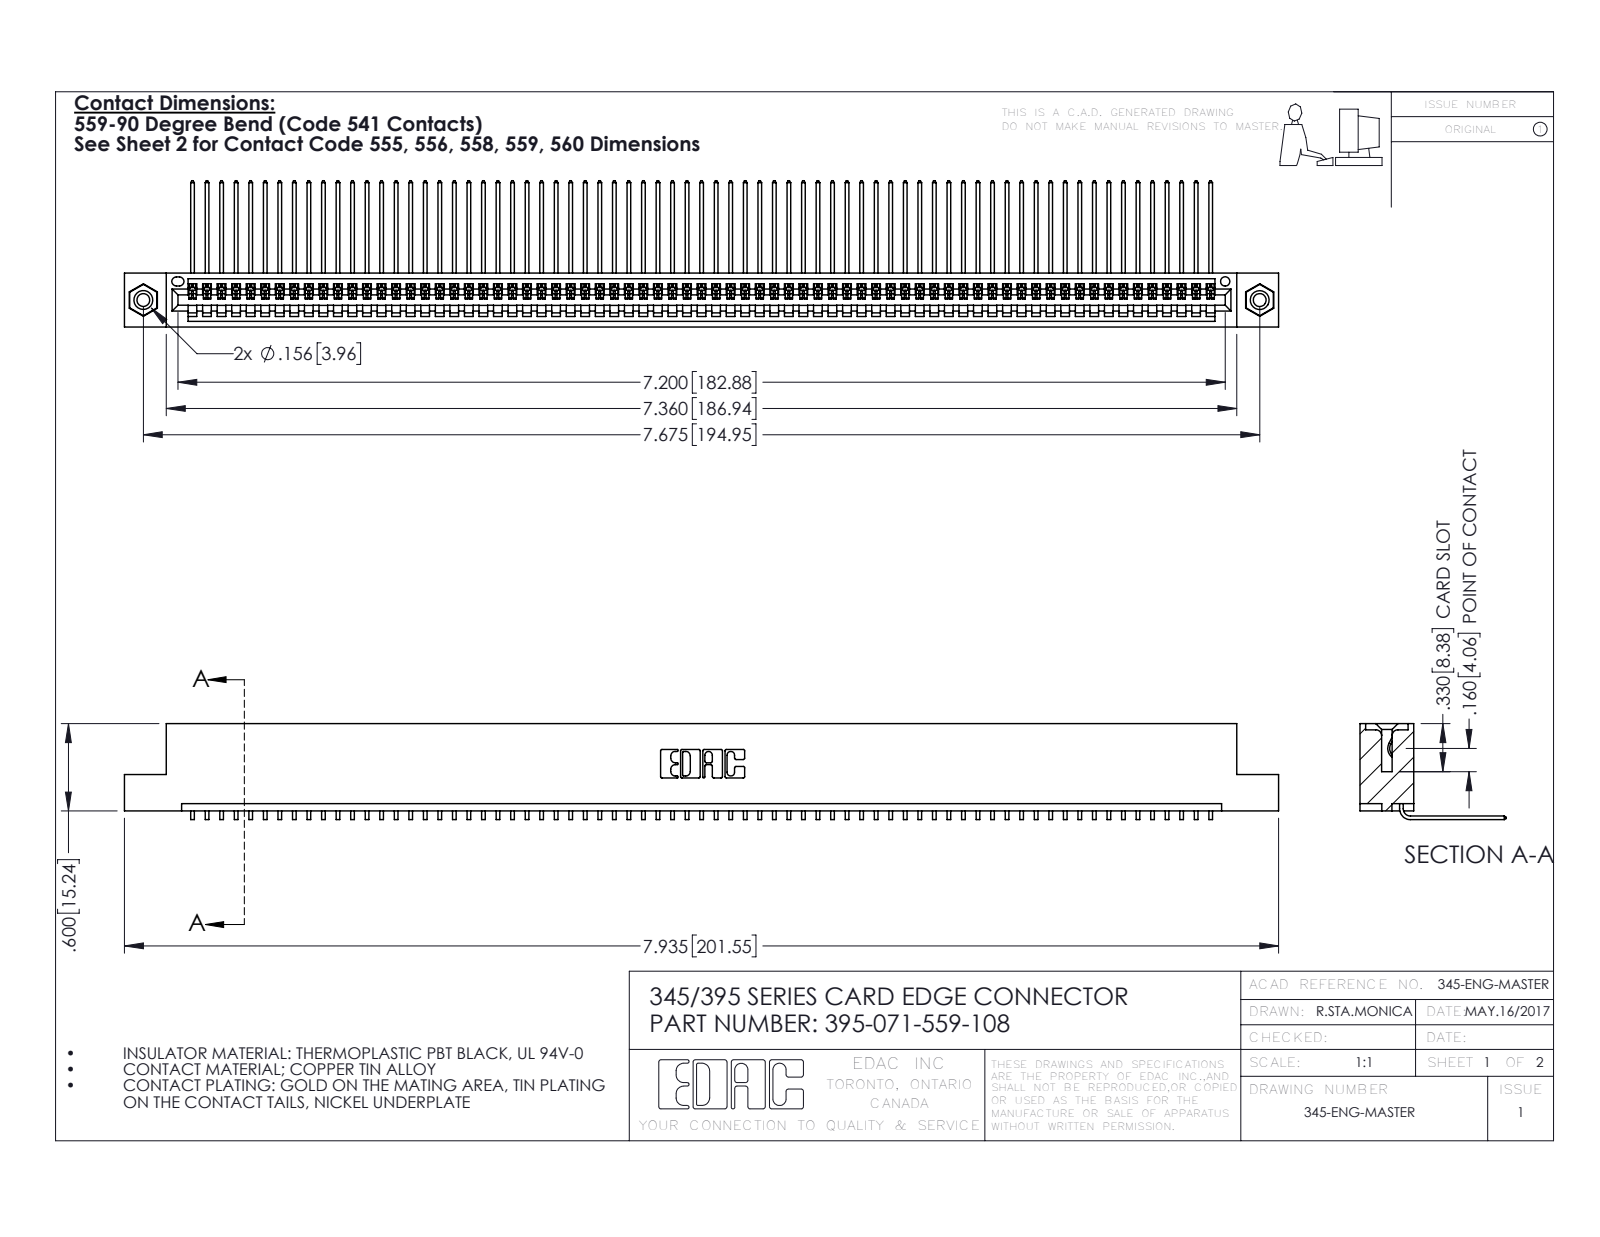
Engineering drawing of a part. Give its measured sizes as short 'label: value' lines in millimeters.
name: 345-250-001_345-250-003-102; 345 Part_Flush Mounting Lugs - 0.156 Dia-TI; 395-071-559-108; 345-292-001_558 559 Tail - 1
written by: SolidWorks 2016 (CONFIG_CONTROL_DESIGN)
unit: mm
bodies: 74 solids, 4446 faces (3094 planar, 1336 cylindrical, 16 other)
size: 201.5 × 25.5 × 16.7
volume: 19 620 mm³; area: 27 860 mm²
holes: 2× ⌀2.3, 2× ⌀3.2, 2× ⌀4, 1× ⌀1.6
bosses: 2× ⌀3.9
rounds: 142× R0.2, 22× R0.3, 6× R0.2, 6× R0.8, 3× R0.7, 2× R0.8, 2× R1, 1× R0.4
face distances: 1.8, 7.6, 9.4, 5.1, 2.5, 6.9, 0.6, 5.7, 3.8, 1.8
hole spacings: 6.9, 189, 194.9
